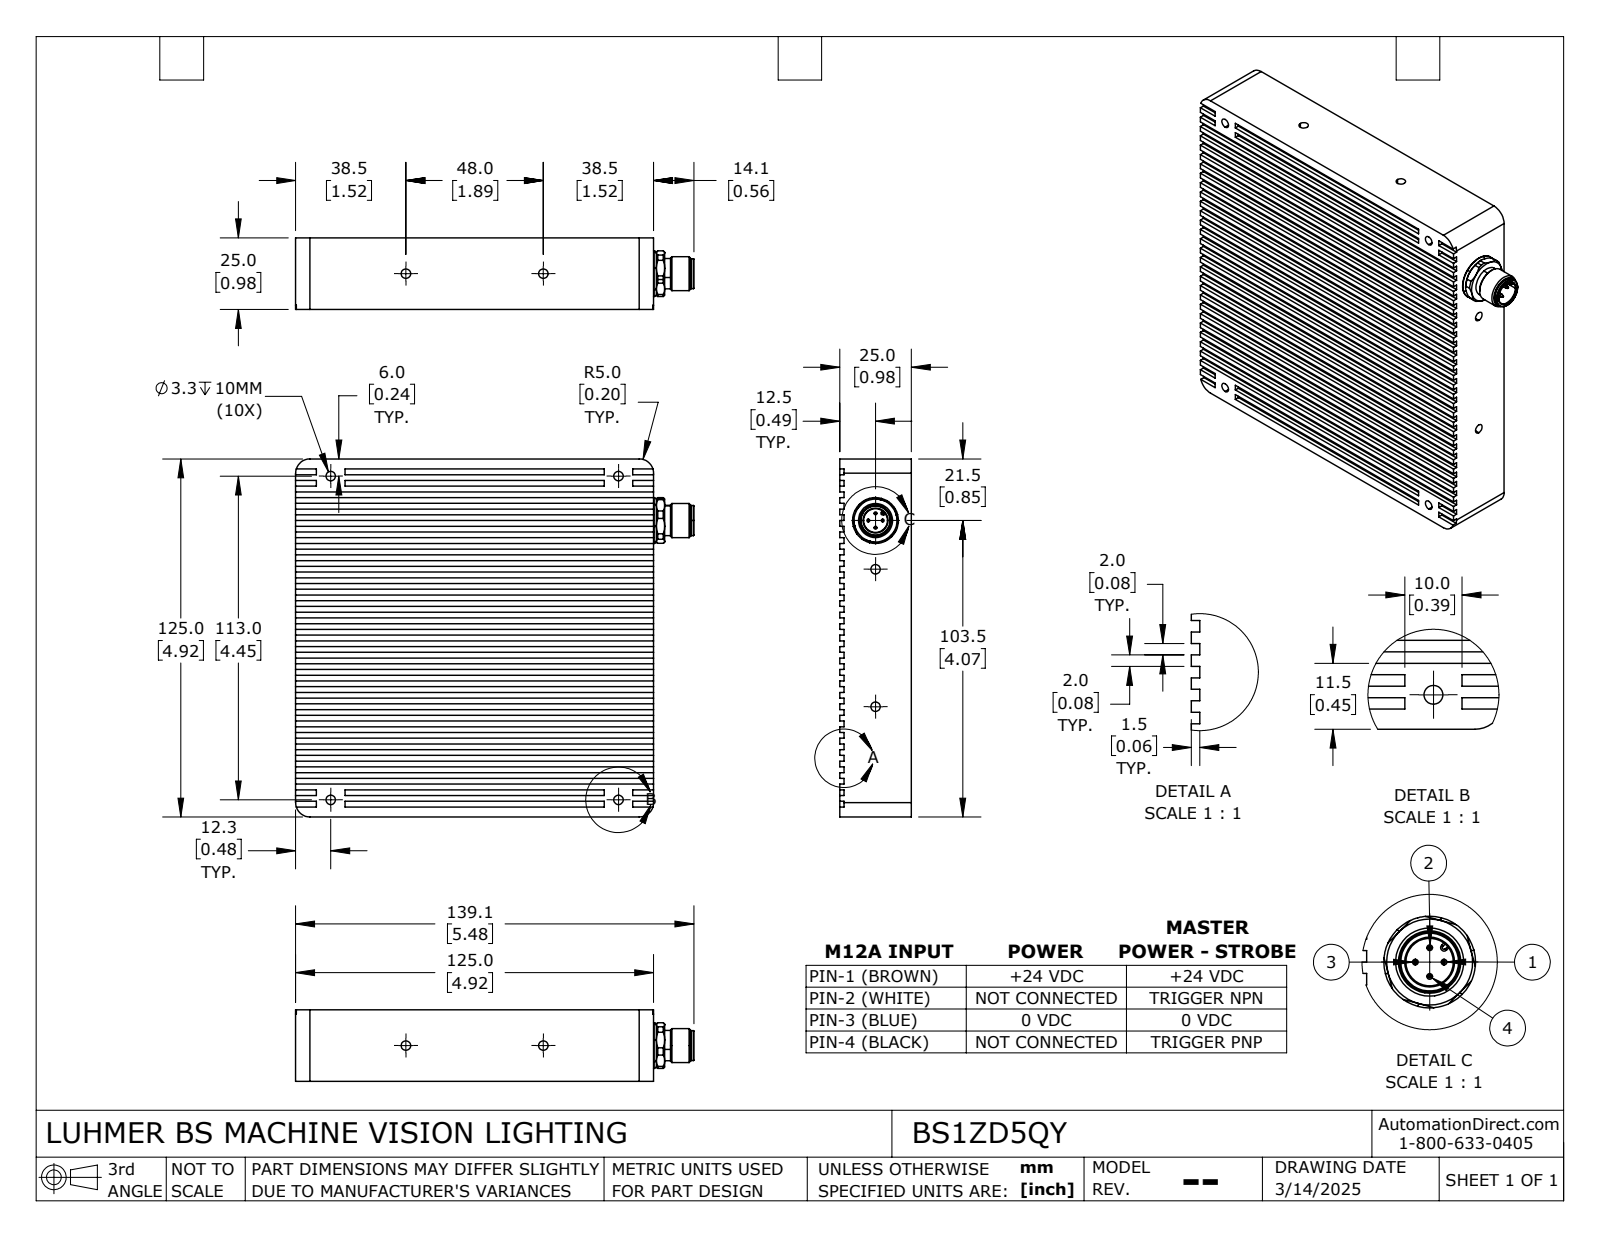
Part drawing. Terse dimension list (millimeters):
name: BS1__5_Y
written by: SolidWorks 2024 (AUTOMOTIVE_DESIGN)
unit: mm
bodies: 1 solid, 1123 faces (229 planar, 562 cylindrical, 332 other)
size: 139.1 × 125 × 25
volume: 370 954 mm³; area: 57 854 mm²
holes: 12× ⌀3.4, 8× ⌀3.3, 4× ⌀1.45, 1× ⌀8.3, 1× ⌀9.4
bosses: 12× ⌀5.6, 12× ⌀2.9, 12× ⌀0.8, 4× ⌀1.4, 4× ⌀1, 1× ⌀16, 1× ⌀11.9, 1× ⌀10.6
rounds: 144× R0.57, 72× R0.25, 12× R1.02, 4× R2, 4× R3.5, 4× R5, 2× R0.3, 1× R0.6
face distances: 24.5, 1.5, 23, 125, 4, 8, 12, 16, 20, 124.6
hole spacings: 134.57, 2.5, 3.54, 5.41, 37.05, 37.07, 37.08, 74.11
